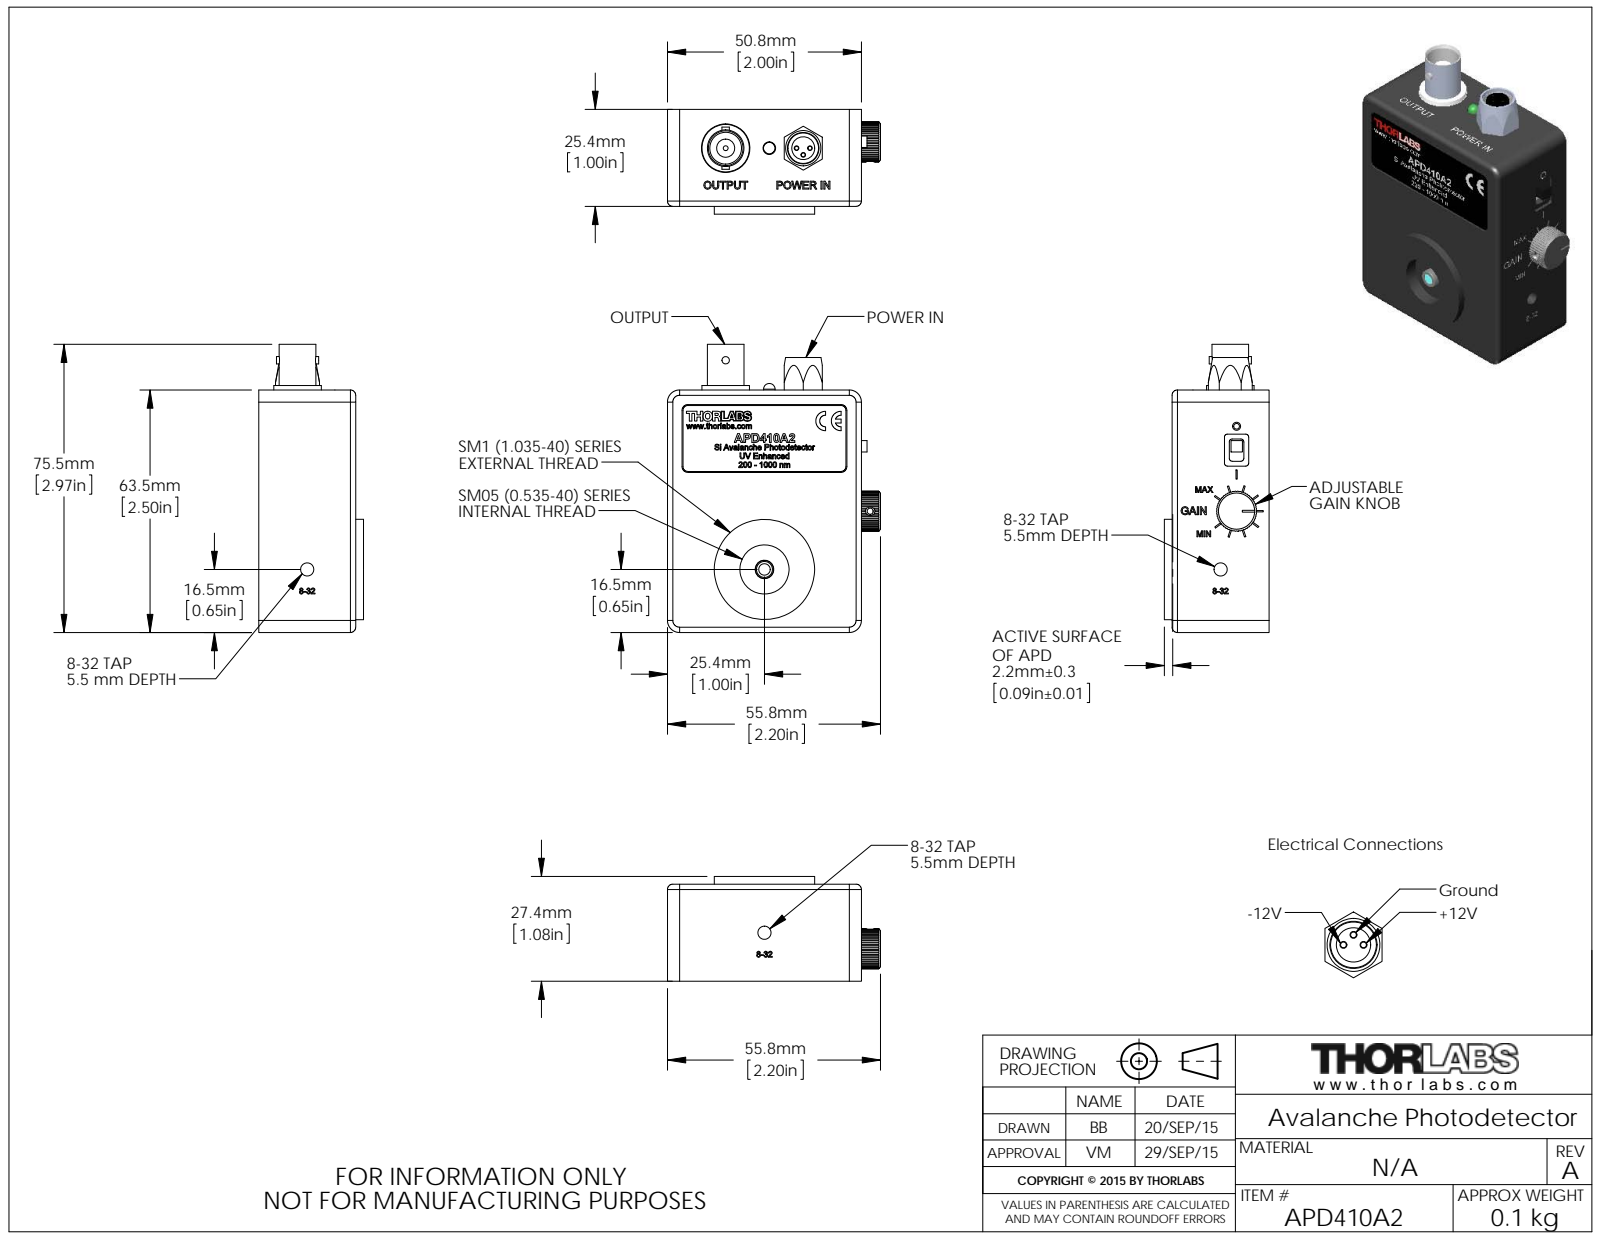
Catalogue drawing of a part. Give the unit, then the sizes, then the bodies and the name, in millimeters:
Units: millimetres
Overall size (bounding box): 75.46 × 55.8 × 27.43
Round holes (diameter × count): ⌀1.6 ×9, ⌀0.51 ×6, ⌀2.4 ×4, ⌀0.45 ×2, ⌀2.5 ×2, ⌀3.45 ×2, ⌀1.27 ×1, ⌀1.32 ×1, ⌀2.1 ×1, ⌀3 ×1, ⌀3.3 ×1, ⌀3.5 ×1
Round bosses / shafts (diameter × count): ⌀1 ×5, ⌀3.8 ×4, ⌀2 ×4, ⌀1.64 ×2, ⌀1.6 ×2, ⌀1.3 ×2, ⌀26.29 ×1, ⌀12.45 ×1
Partial cylindrical surfaces — rounded edges, fillets, slot ends (radius × count): R0.3 ×53, R3.17 ×19, R3.3 ×14, R0.79 ×8, R2.41 ×8, R0.5 ×6, R1.91 ×6, R0.2 ×5
Main face-to-face distances: 1.59, 2.54, 0.4, 23.75, 22.16, 1.65, 25.4, 23.81, 25, 23.41
Hole centre spacings: 41.17, 4.41, 51.14, 65.51, 2.49, 43.46, 1.27, 2
Bodies: 0 solids, 2545 faces (1308 planar, 436 cylindrical, 801 other)
Part name (STEP PRODUCT): MTN005411
STEP written by: SolidWorks 2014 (CONFIG_CONTROL_DESIGN)
